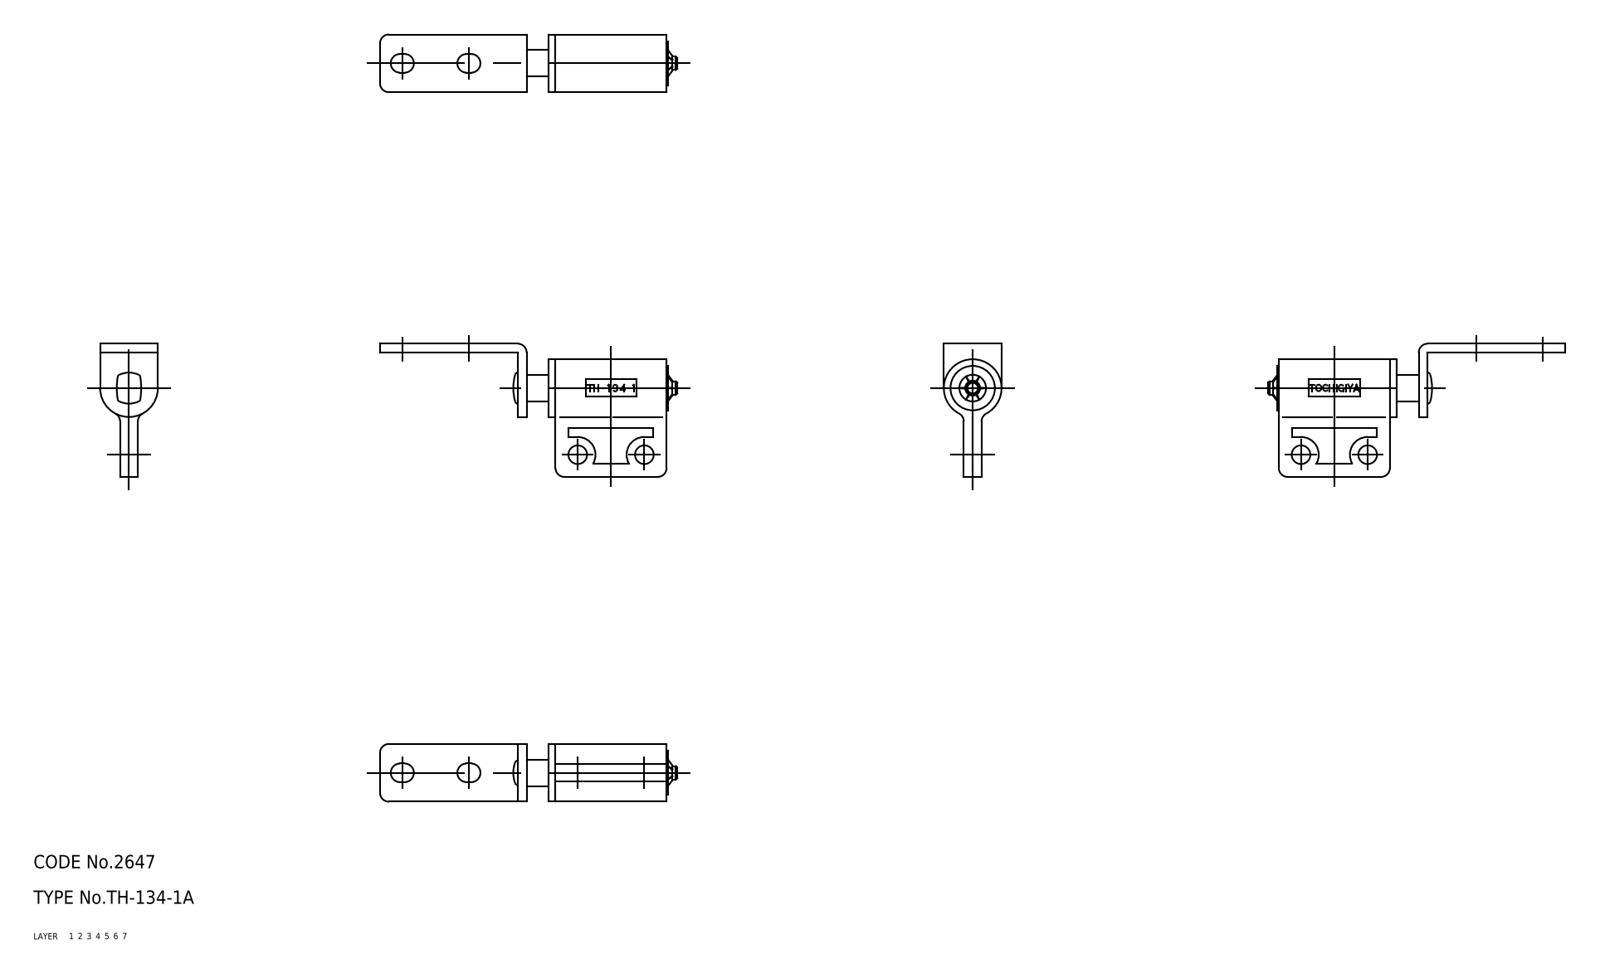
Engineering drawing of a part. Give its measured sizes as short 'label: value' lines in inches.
name: shaft; retainer; case; bracket (+1 more)
written by: CADfix (AUTOMOTIVE_DESIGN)
unit: in
bodies: 4 solids, 137 faces (0 planar, 0 cylindrical, 137 other)
size: 2.634 × 1.181 × 0.512
volume: 0.333 in³; area: 8.103 in²
